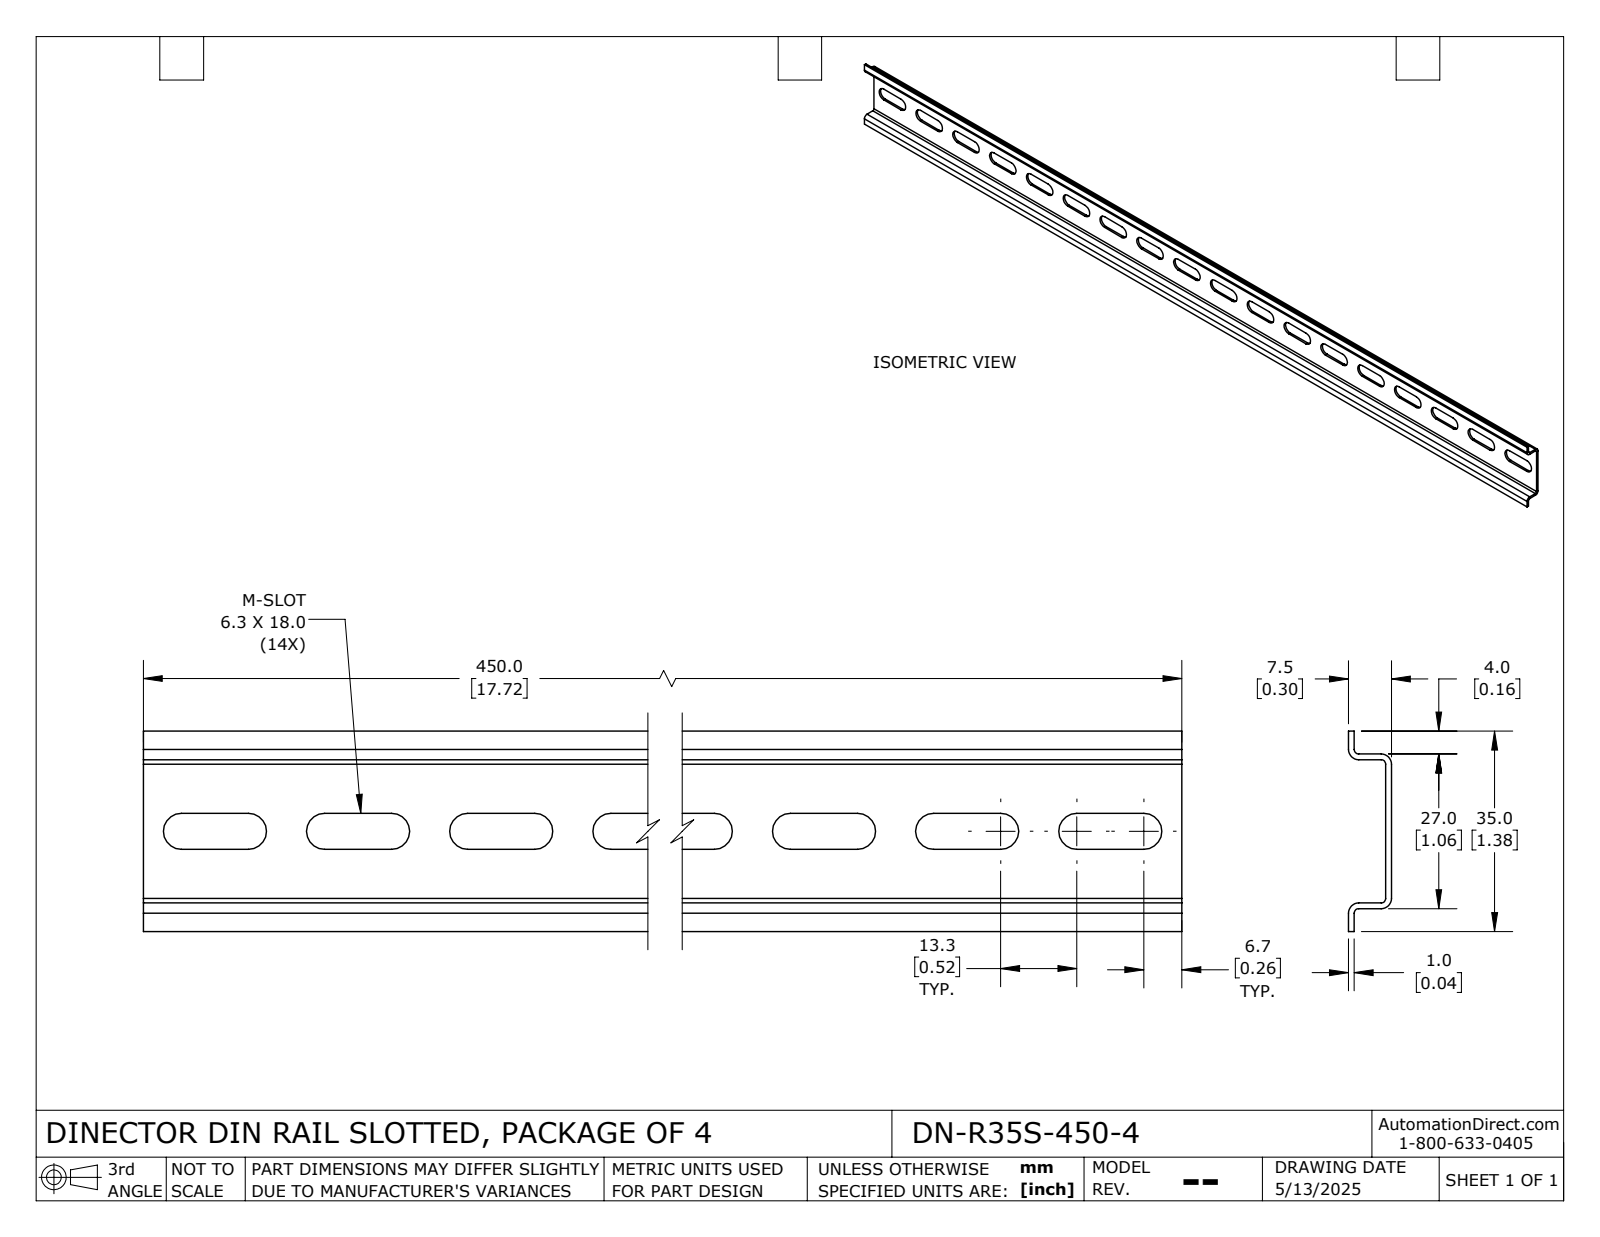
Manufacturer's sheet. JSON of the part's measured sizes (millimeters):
{"part_name": "DN-R35S-450-4_Default", "step_written_by": "SolidWorks 2024 (CONFIG_CONTROL_DESIGN)", "units": "millimeters", "bodies": {"solids": 1, "faces": 94, "planar": 50, "cylindrical": 44, "other": 0}, "overall_size": [450, 35, 7.5], "volume_mm3": 18708, "surface_area_mm2": 39185, "partial_cylinders_radius": [[3.15, 36], [0.8, 4], [1.8, 4]], "face_to_face_distances": [1, 6.5, 26, 7.5, 5.5, 27, 25, 4, 5, 30]}
